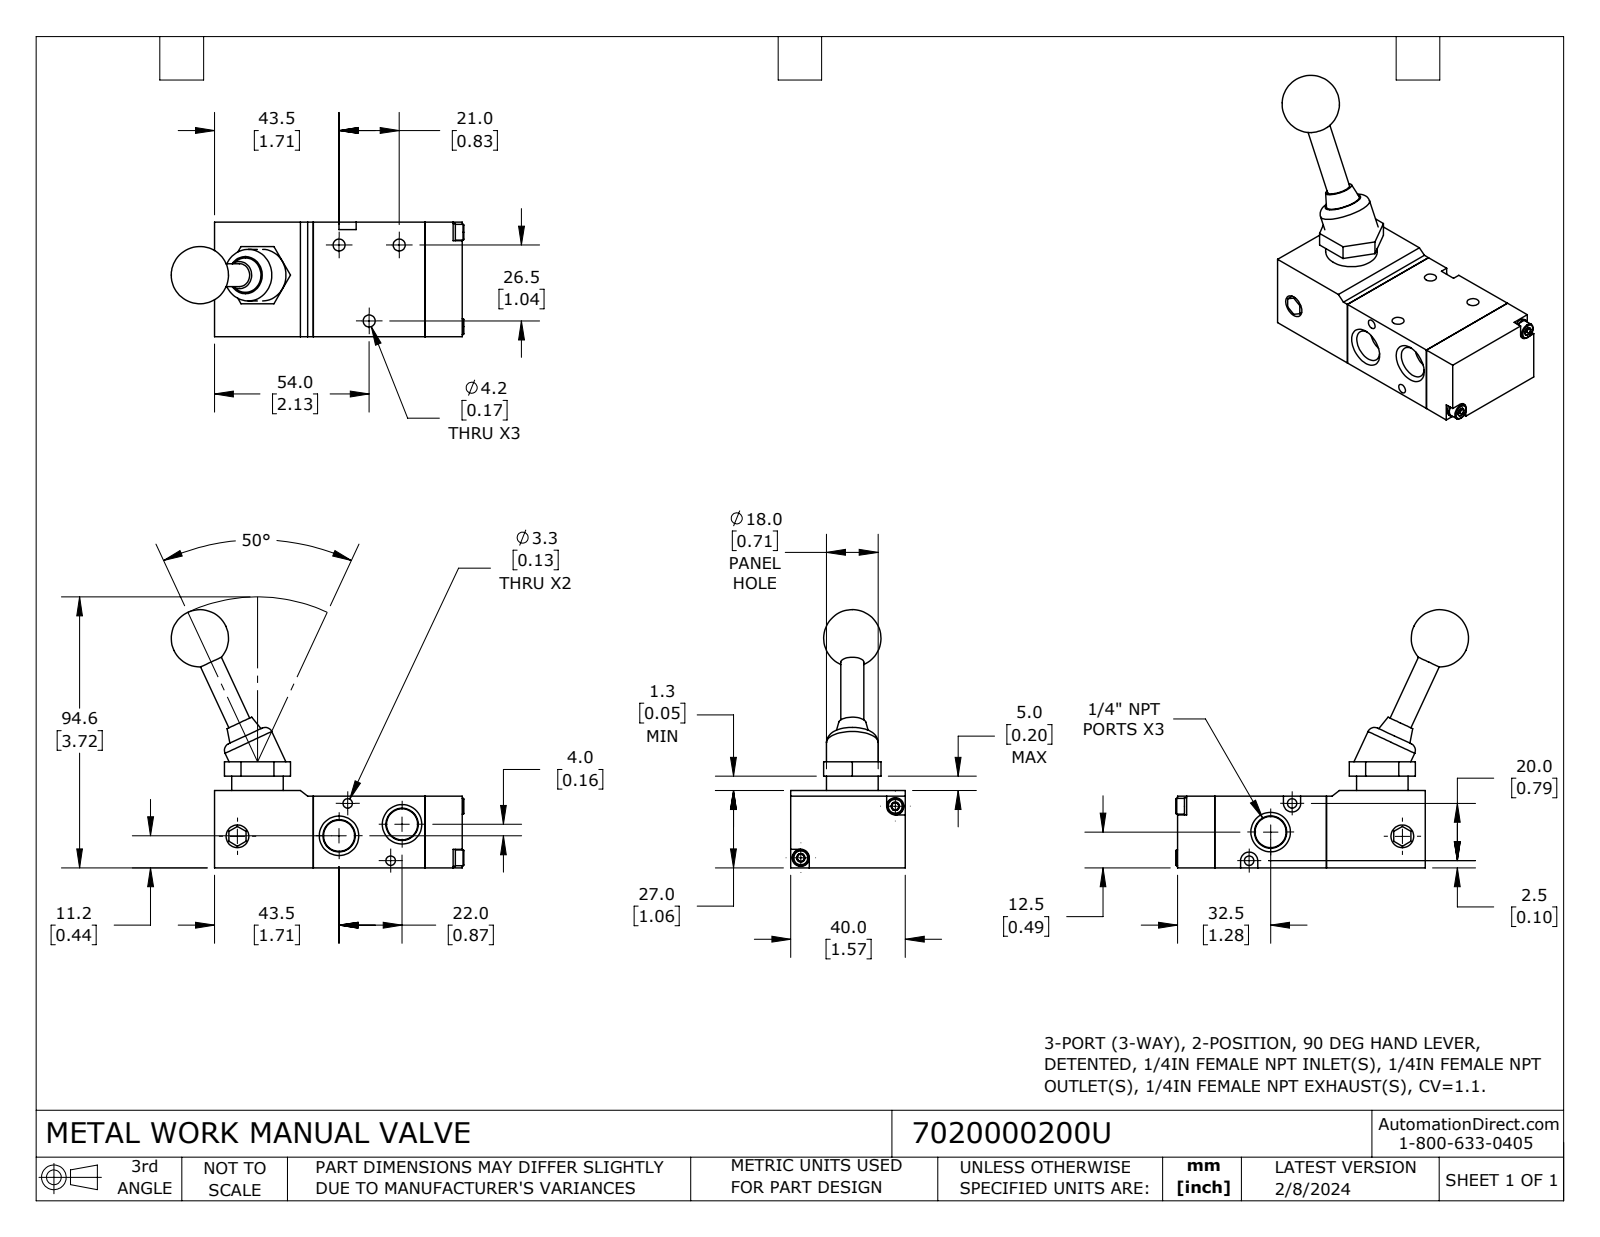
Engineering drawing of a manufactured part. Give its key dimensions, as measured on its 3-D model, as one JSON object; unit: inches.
{"part_name": "7020000200U", "step_written_by": "SolidWorks 2023 (CONFIG_CONTROL_DESIGN)", "units": "inches", "bodies": {"solids": 8, "faces": 183, "planar": 96, "cylindrical": 41, "other": 46}, "overall_size": [4.024, 3.549, 1.575], "volume_in3": 5.925, "surface_area_in2": 38.19, "round_holes": [[0.165, 3], [0.118, 2], [0.13, 2], [0.313, 1]], "round_bosses_or_shafts": [[0.709, 2], [0.236, 2], [0.217, 2], [0.315, 1]], "partial_cylinders_radius": [[0.118, 2]], "face_to_face_distances": [0.984, 1.535, 1.575, 2.894, 1.358, 1.063, 0.079, 0.512, 2.047, 3.406], "hole_center_spacings": [1.122, 0.827, 0.984, 1.48, 1.582, 2.133]}
